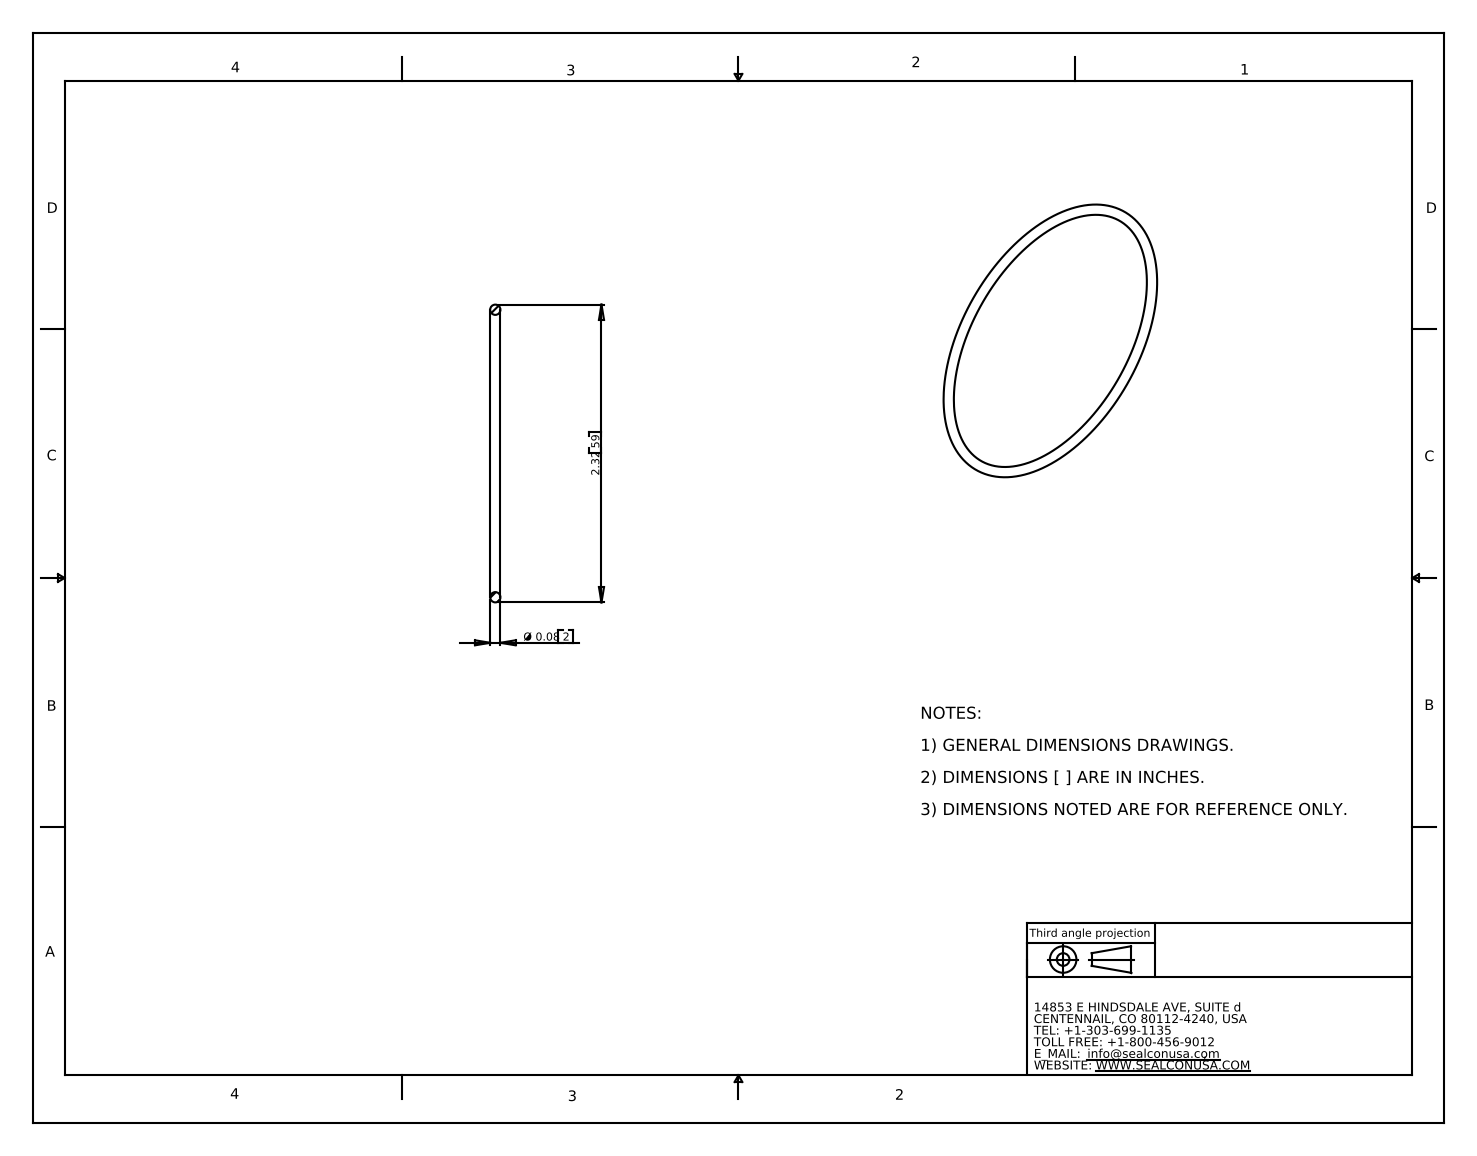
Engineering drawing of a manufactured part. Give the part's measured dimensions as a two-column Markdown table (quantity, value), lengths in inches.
| quantity | value |
| --- | --- |
| part name | OM-63-VT |
| STEP written by | SolidWorks 2007 (CONFIG_CONTROL_DESIGN) |
| units | inches |
| bodies | 1 solid, 4 faces (0 planar, 0 cylindrical, 4 other) |
| overall size | 2.32 × 2.32 × 0.08 |
| volume | 0.035 in³ |
| surface area | 1.769 in² |
